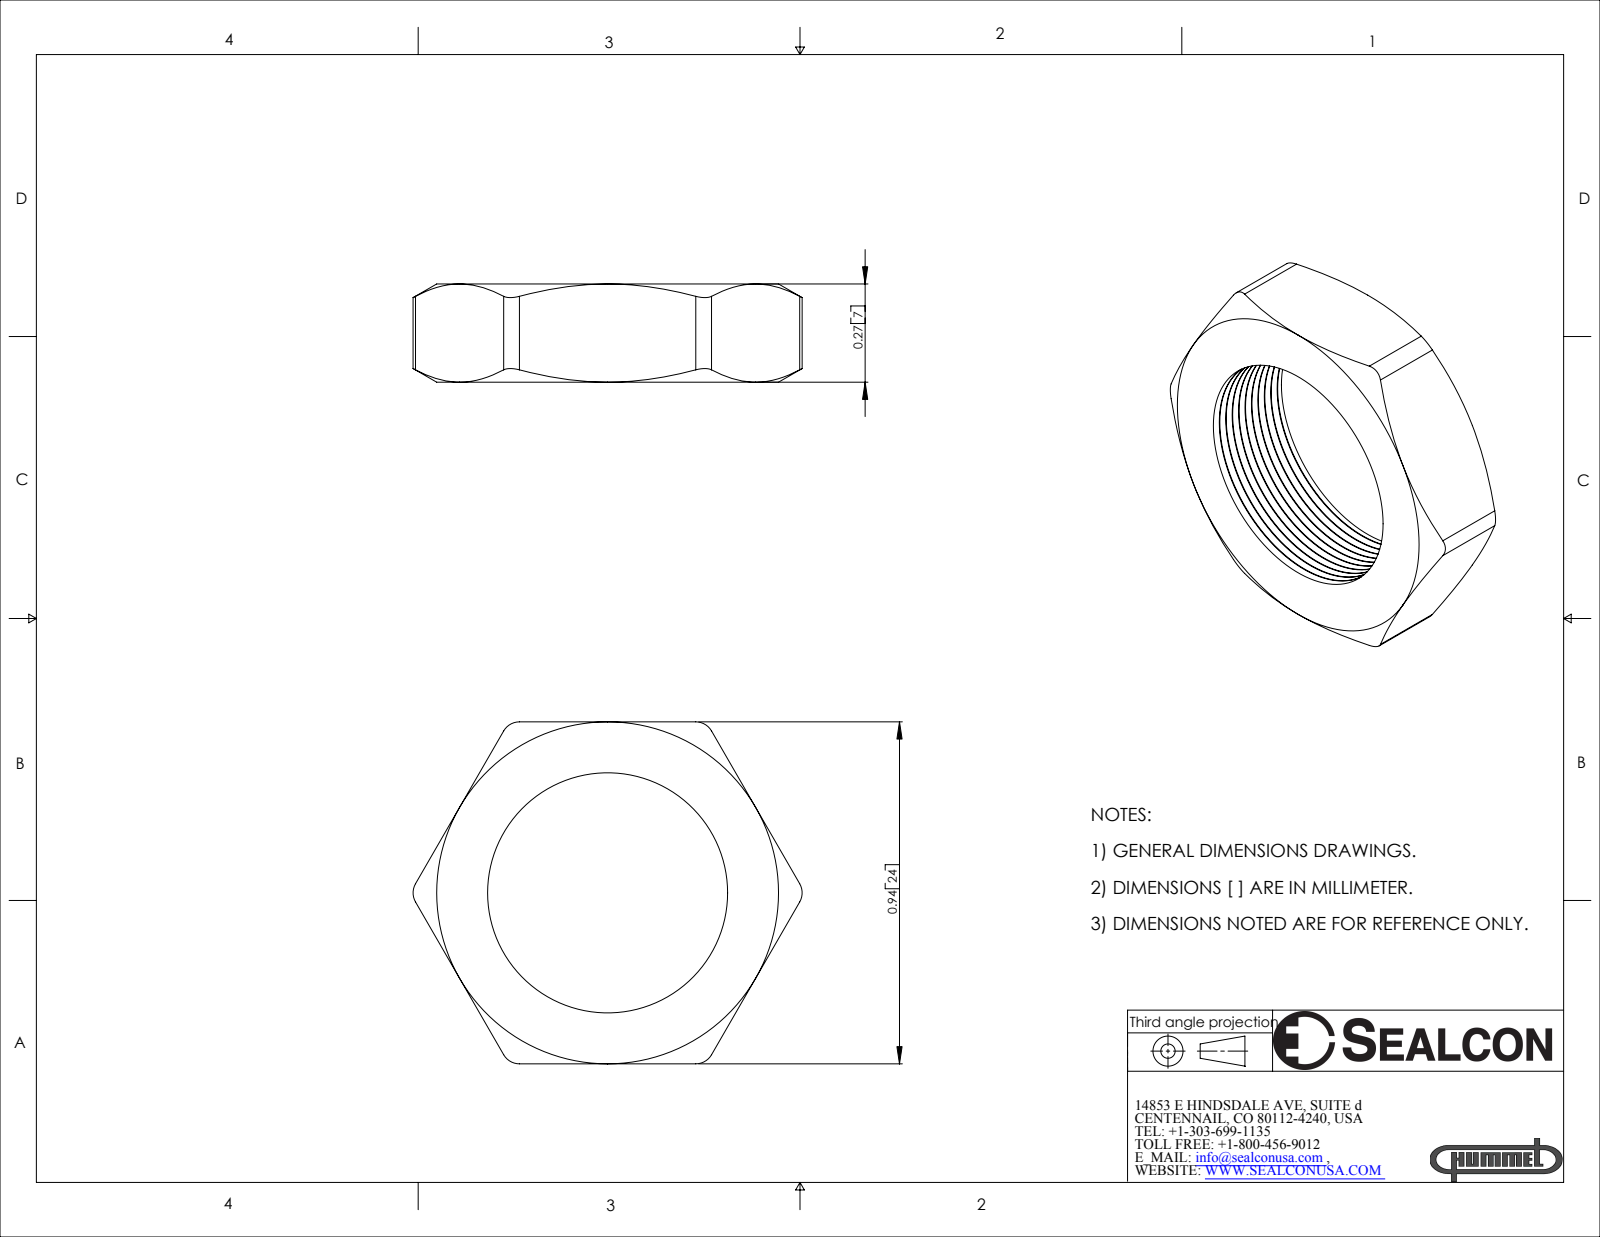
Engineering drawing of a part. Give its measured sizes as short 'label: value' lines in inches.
name: NN-09
written by: SolidWorks 2007 (CONFIG_CONTROL_DESIGN)
unit: in
bodies: 1 solid, 93 faces (8 planar, 27 cylindrical, 58 other)
size: 1.07 × 0.94 × 0.27
volume: 0.107 in³; area: 2.747 in²
holes: 1× ⌀0.66
rounds: 6× R0.05
face distances: 0.94, 0.27
